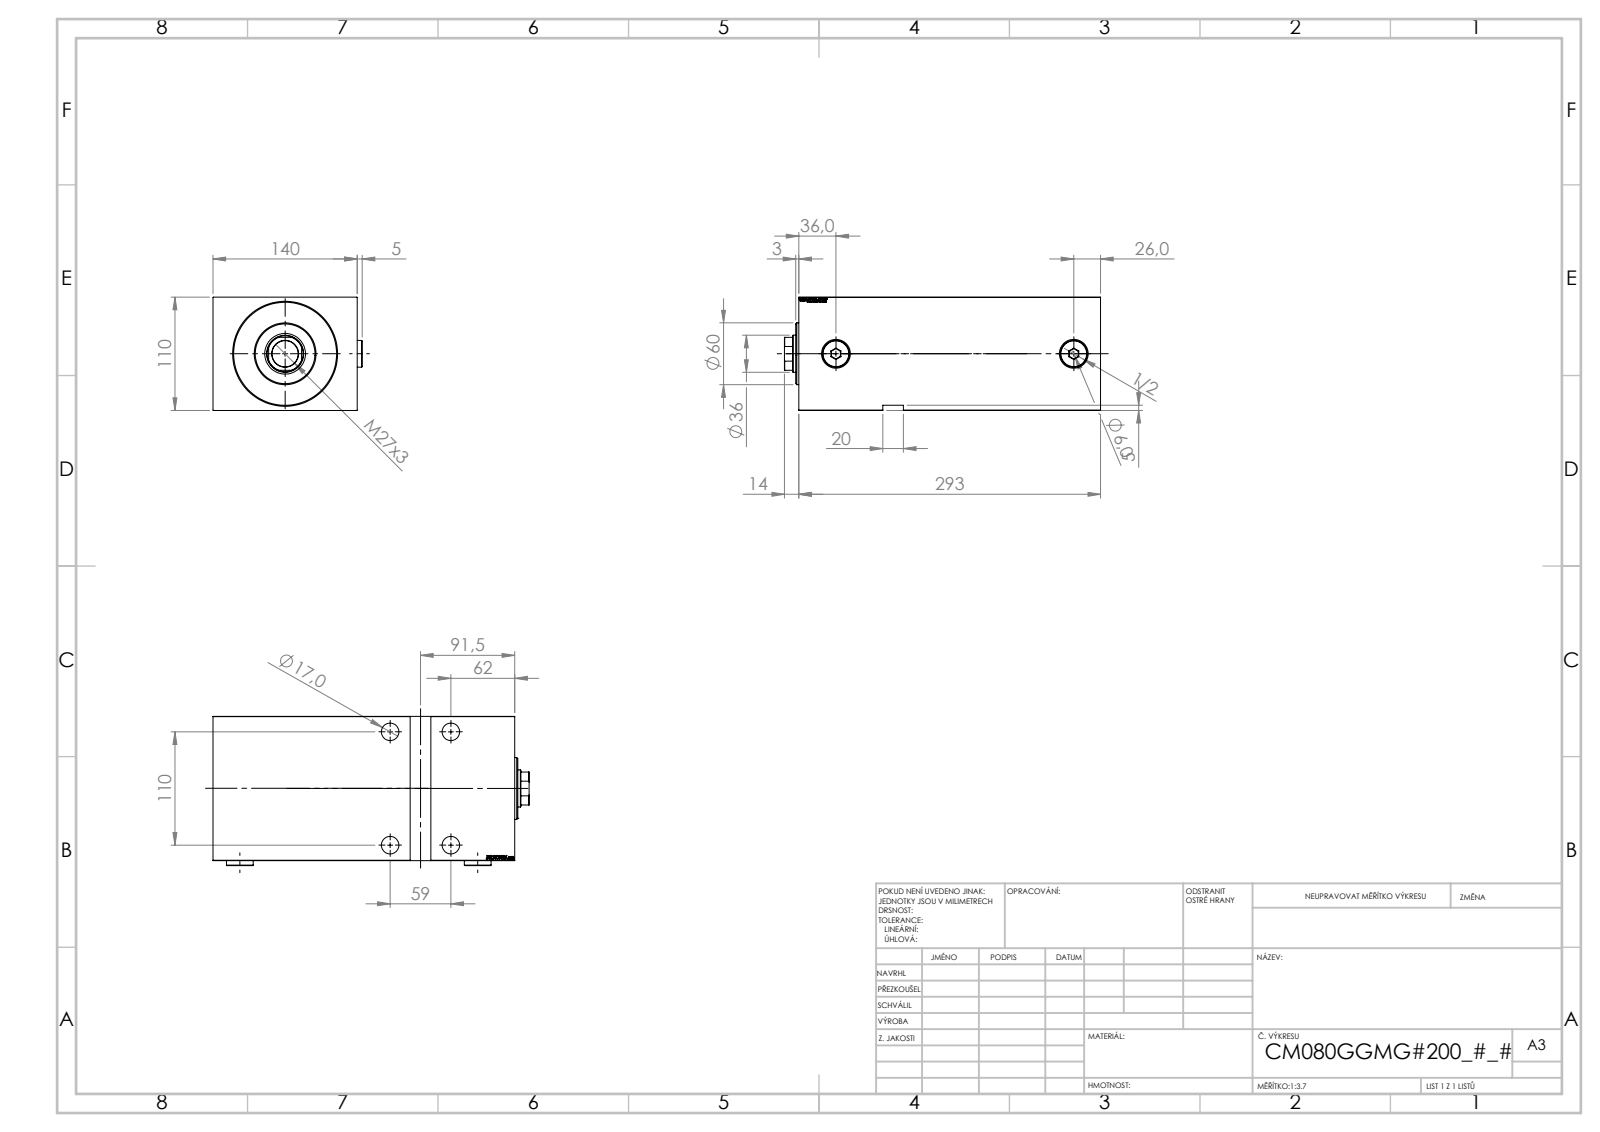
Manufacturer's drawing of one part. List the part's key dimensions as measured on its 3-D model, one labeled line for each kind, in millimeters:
Part name (STEP PRODUCT): V450CM_G_VCP; Zatka_OIL_PORT; V450CM_VC_G; V450CM_G_Body
STEP written by: SolidWorks 2019 (CONFIG_CONTROL_DESIGN)
Units: millimetres
Bodies: 5 solids, 896 faces (442 planar, 56 cylindrical, 398 other)
Overall size (bounding box): 307 × 144.9 × 110
Volume: 3 527 000 mm³ · Surface area: 345 937 mm²
Round holes (diameter × count): ⌀17 ×4, ⌀25 ×4, ⌀6 ×2, ⌀20.96 ×2, ⌀28 ×2, ⌀25.5 ×1, ⌀36 ×1, ⌀39.5 ×1, ⌀80 ×1, ⌀82 ×1, ⌀100 ×1
Round bosses / shafts (diameter × count): ⌀26 ×2, ⌀60 ×1
Partial cylindrical surfaces — rounded edges, fillets, slot ends (radius × count): R17.5 ×1
Main face-to-face distances: 110, 140, 5, 293, 21, 272, 288, 267, 79, 58
Hole centre spacings: 59, 110, 124.82, 231
